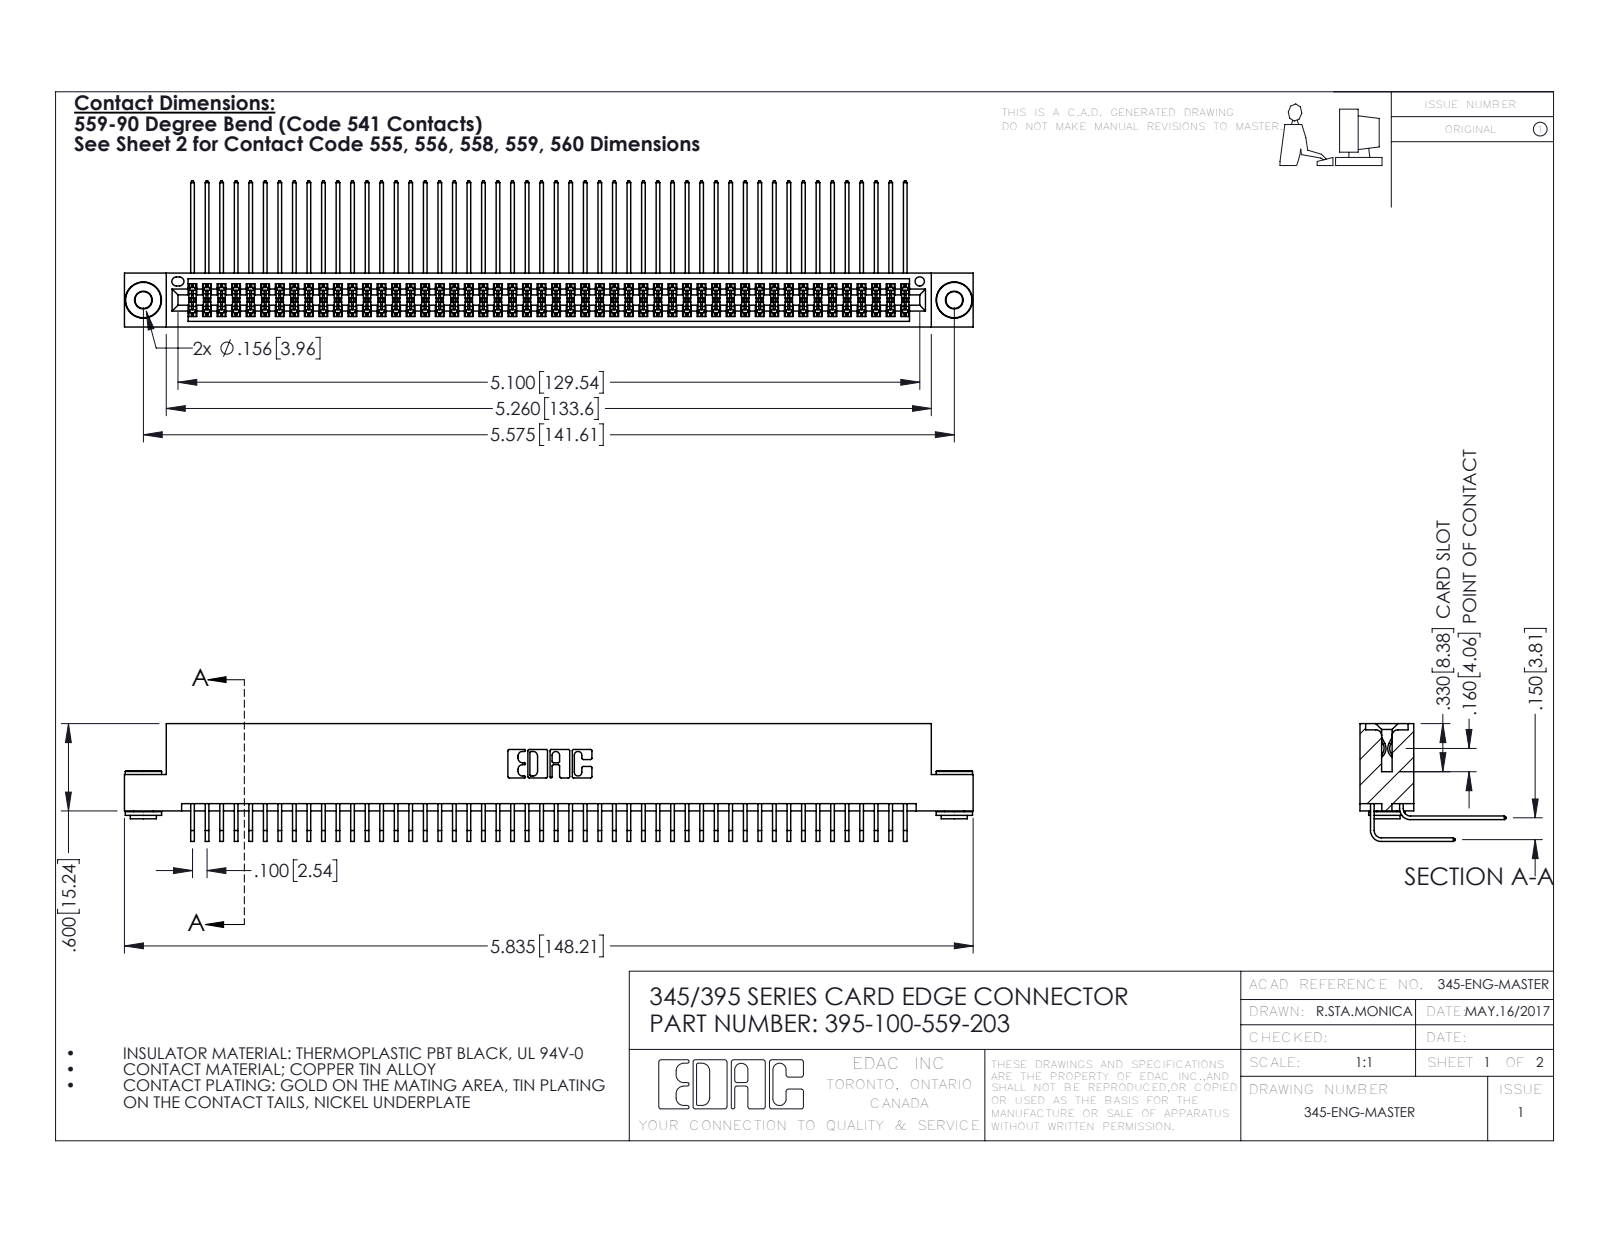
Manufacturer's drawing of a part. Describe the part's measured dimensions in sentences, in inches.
The part is named "345-292-001_559 Tail - 2; 345-250-002_345-250-002-102; 345 Part_Flush Mounting Lugs - 0.156 Dia-TH; 395-100-559-203 (+1 more)". Its 3-D file was written by "SolidWorks 2016 (CONFIG_CONTROL_DESIGN)". It is 103 solids with 5364 faces: 3590 planar, 1766 cylindrical and 8 other. Overall it measures 5.835 by 1.005 by 0.809 inches. Its volume is 0.919 cubic inches and its surface area 39.28 square inches. Round holes: 2 of diameter 0.116, 2 of diameter 0.156, 1 of diameter 0.064. Round bosses or shafts: 2 of diameter 0.25, 2 of diameter 0.18, 2 of diameter 0.136. Partial cylindrical surfaces (rounded edges, fillets, slot ends): 151 of radius 0.006, 22 of radius 0.01, 6 of radius 0.007, 6 of radius 0.031, 3 of radius 0.026, 2 of radius 0.014, 2 of radius 0.019, 2 of radius 0.022. The main face-to-face distances are 0.072, 0.298, 0.2, 0.37, 0.025, 0.098, 0.272, 0.225, 0.175, 0.15. The hole center spacings are 0.27, 5.339, 5.575.
